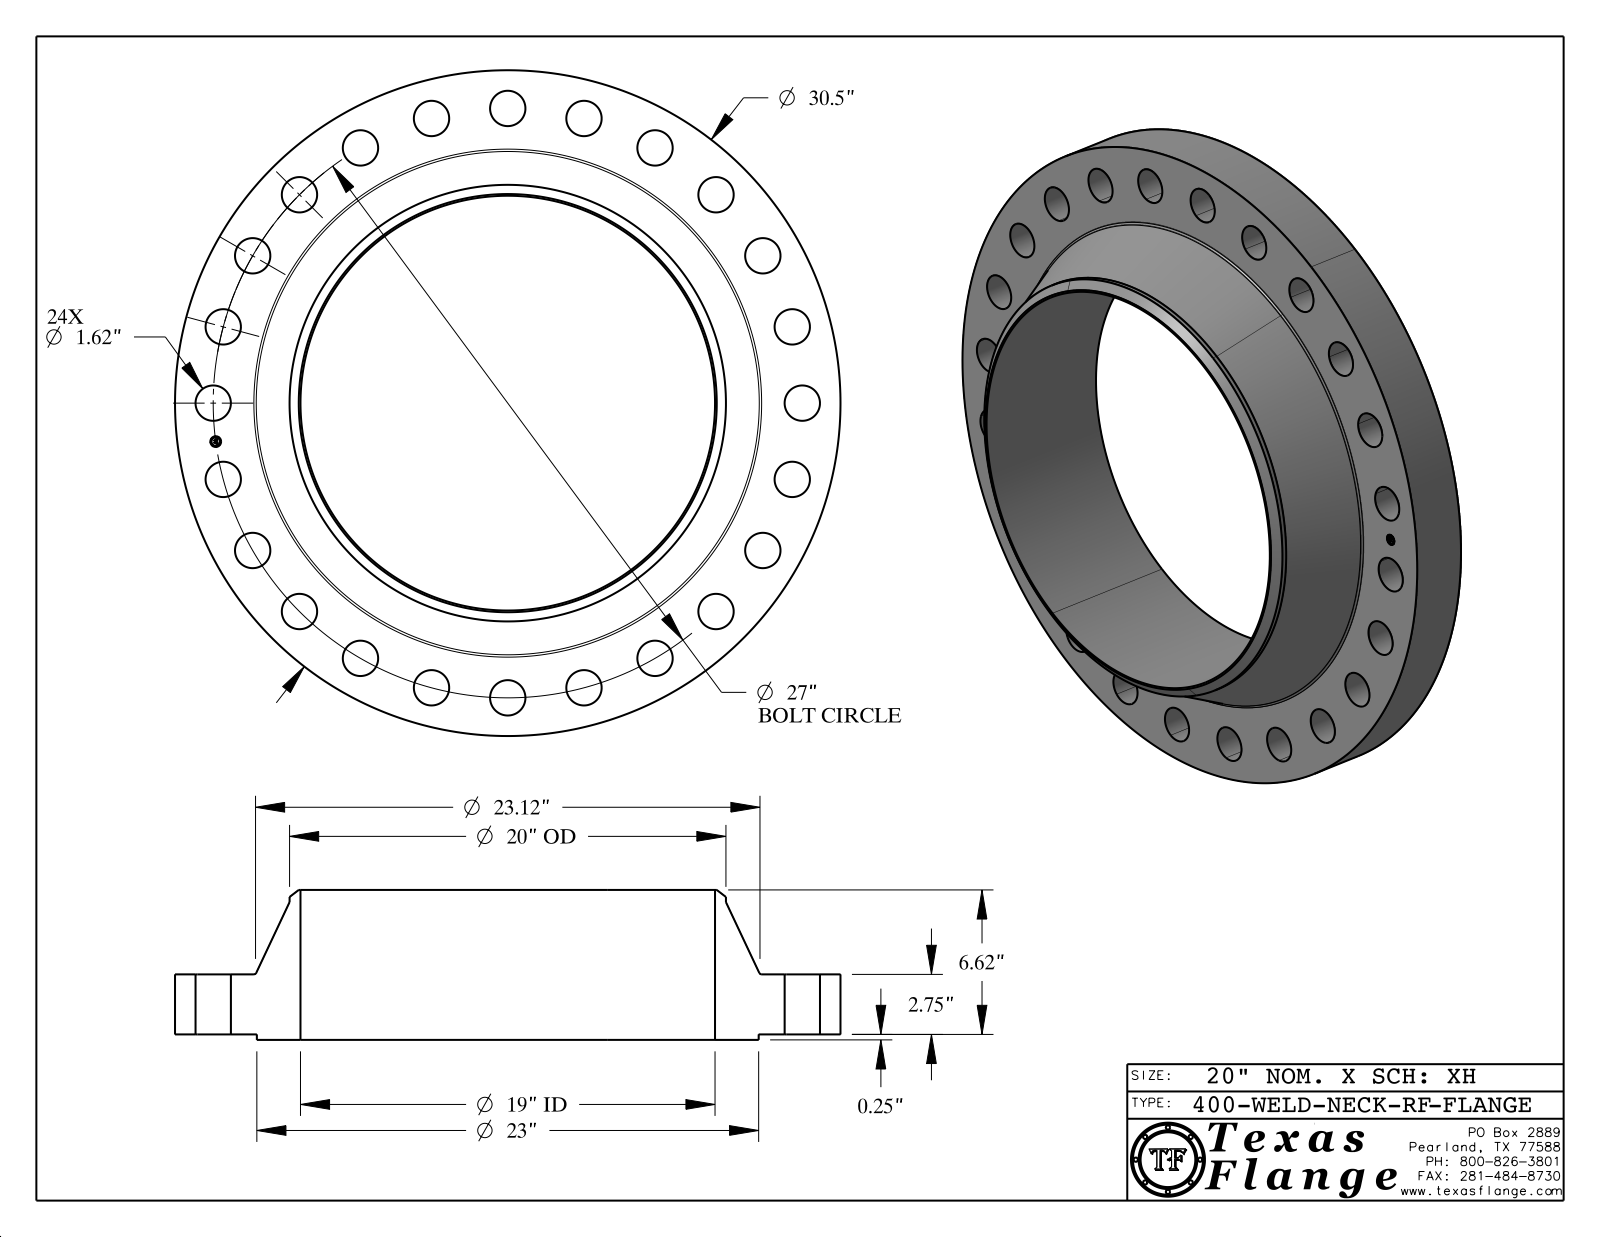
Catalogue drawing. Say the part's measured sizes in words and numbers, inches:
The part is named "400-WELD-NECK-RF". Its 3-D file was written by "CATIA V5 STEP AP214 (AUTOMOTIVE_DESIGN)". It is 1 solid with 451 faces: 369 planar, 76 cylindrical and 6 other. Overall it measures 30.5 by 30.5 by 6.87 inches. Its volume is 1 412 cubic inches and its surface area 1 985 square inches. Round holes: 24 of diameter 1.62, 1 of diameter 0.495, 1 of diameter 19. Round bosses or shafts: 8 of diameter 0.03, 1 of diameter 30.5, 1 of diameter 23, 1 of diameter 20, 1 of diameter 0.39. The main face-to-face distances are 2.75, 0.25, 3, 6.87, 6.62, 3.87, 2.985, 2.735, 0.015, 3.885. The hole center spacings are 13.5, 3.524, 6.988, 10.333, 16.437, 24.945, 26.769, 21.421.
